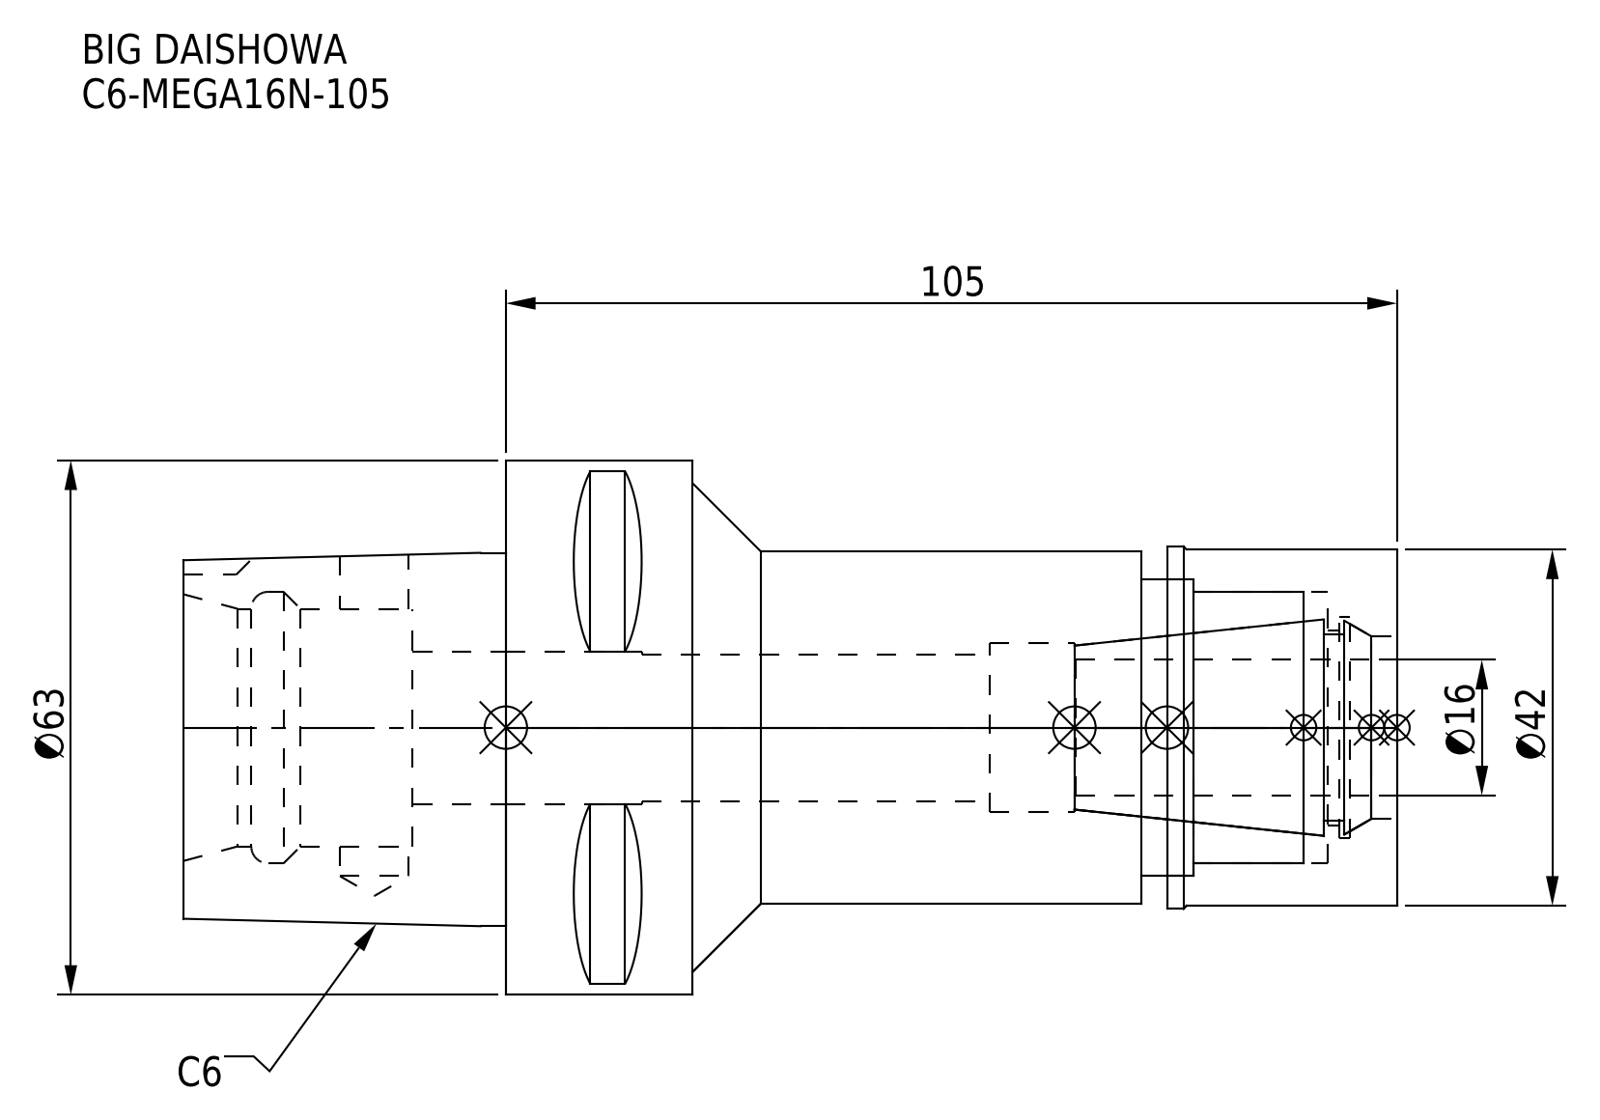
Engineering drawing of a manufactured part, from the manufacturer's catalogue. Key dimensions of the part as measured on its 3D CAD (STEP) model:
Part name (STEP PRODUCT): C6-MEGA16N-105; C6-MEGA16N-105_1.stp; C6-MEGA16N-105-160_ASM.stp; MGN16_1.stp (+3 more)
STEP written by: SolidWorks 2019 (CONFIG_CONTROL_DESIGN)
Units: millimetres
Bodies: 2 solids, 95 faces (38 planar, 39 cylindrical, 18 other)
Overall size (bounding box): 143 × 63 × 63
Volume: 184 841 mm³ · Surface area: 40 986 mm²
Round holes (diameter × count): ⌀8.1 ×1, ⌀17.3 ×1, ⌀18 ×1, ⌀20 ×1, ⌀21.5 ×1, ⌀23 ×1, ⌀26 ×1, ⌀28 ×1, ⌀32 ×1, ⌀35 ×1
Round bosses / shafts (diameter × count): ⌀63 ×1, ⌀42.7 ×1, ⌀42 ×1, ⌀41.6 ×1
Partial cylindrical surfaces — rounded edges, fillets, slot ends (radius × count): R5 ×1
Main face-to-face distances: 105, 11, 38, 83, 22, 143, 60, 27.1, 55.9, 77.9
